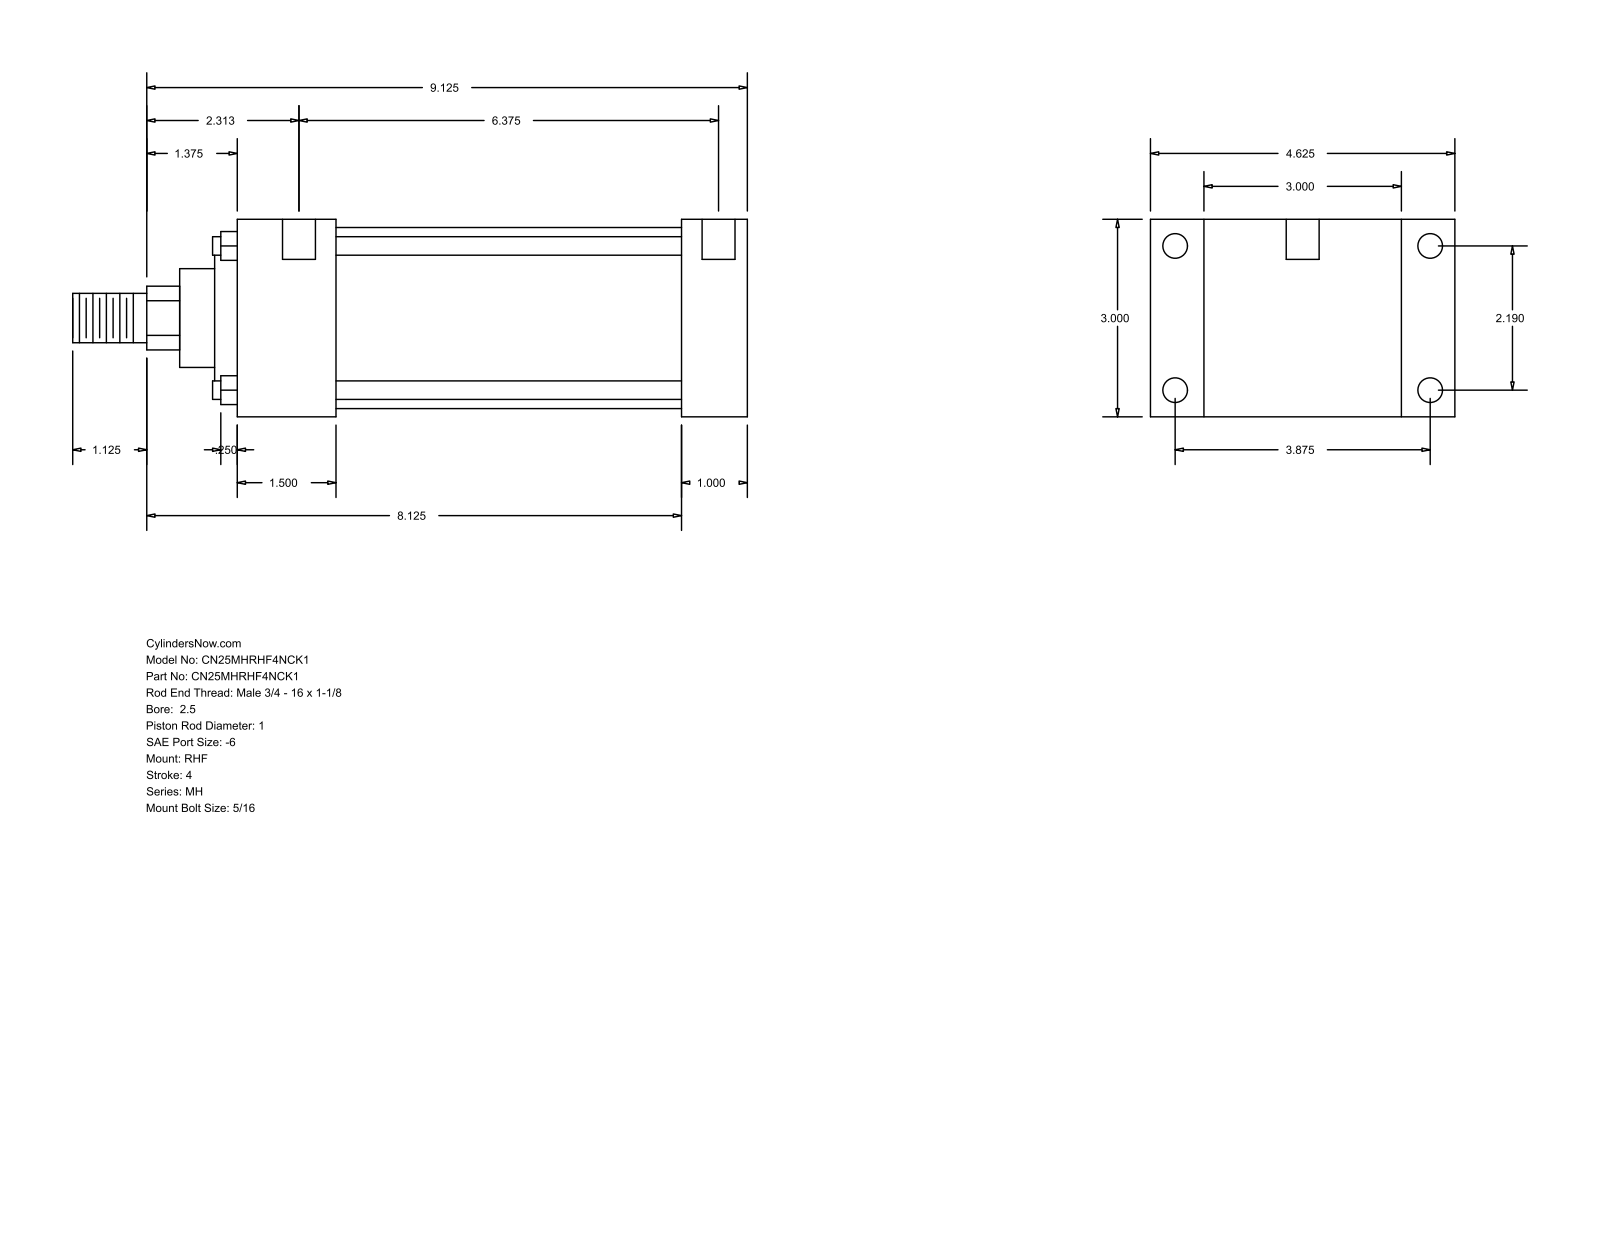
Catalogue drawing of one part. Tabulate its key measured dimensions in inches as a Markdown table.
| quantity | value |
| --- | --- |
| part name | MH_RHF__0250_1 |
| STEP written by | GSSL Pune (CONFIG_CONTROL_DESIGN) |
| units | inches |
| bodies | 0 solids, 90 faces (61 planar, 29 cylindrical, 0 other) |
| overall size | 10.25 × 4.625 × 3 |
| round holes (diameter × count) | 0.219 × 4, 0.375 × 4, 0.5 × 2 |
| round bosses / shafts (diameter × count) | 0.281 × 4, 2.75 × 1, 2.375 × 1, 1.5 × 1, 1 × 1, 0.75 × 1 |
| partial cylindrical surfaces (radius × count) | 0.484 × 1 |
| main face-to-face distances | 3, 1, 0.813, 3.813, 6.75, 7.75, 4.625, 1.5, 5.25, 6.25 |
| hole center spacings | 2.19, 3.875, 4.451, 6.687, 0.125, 0.187, 6.375, 6.5 |
